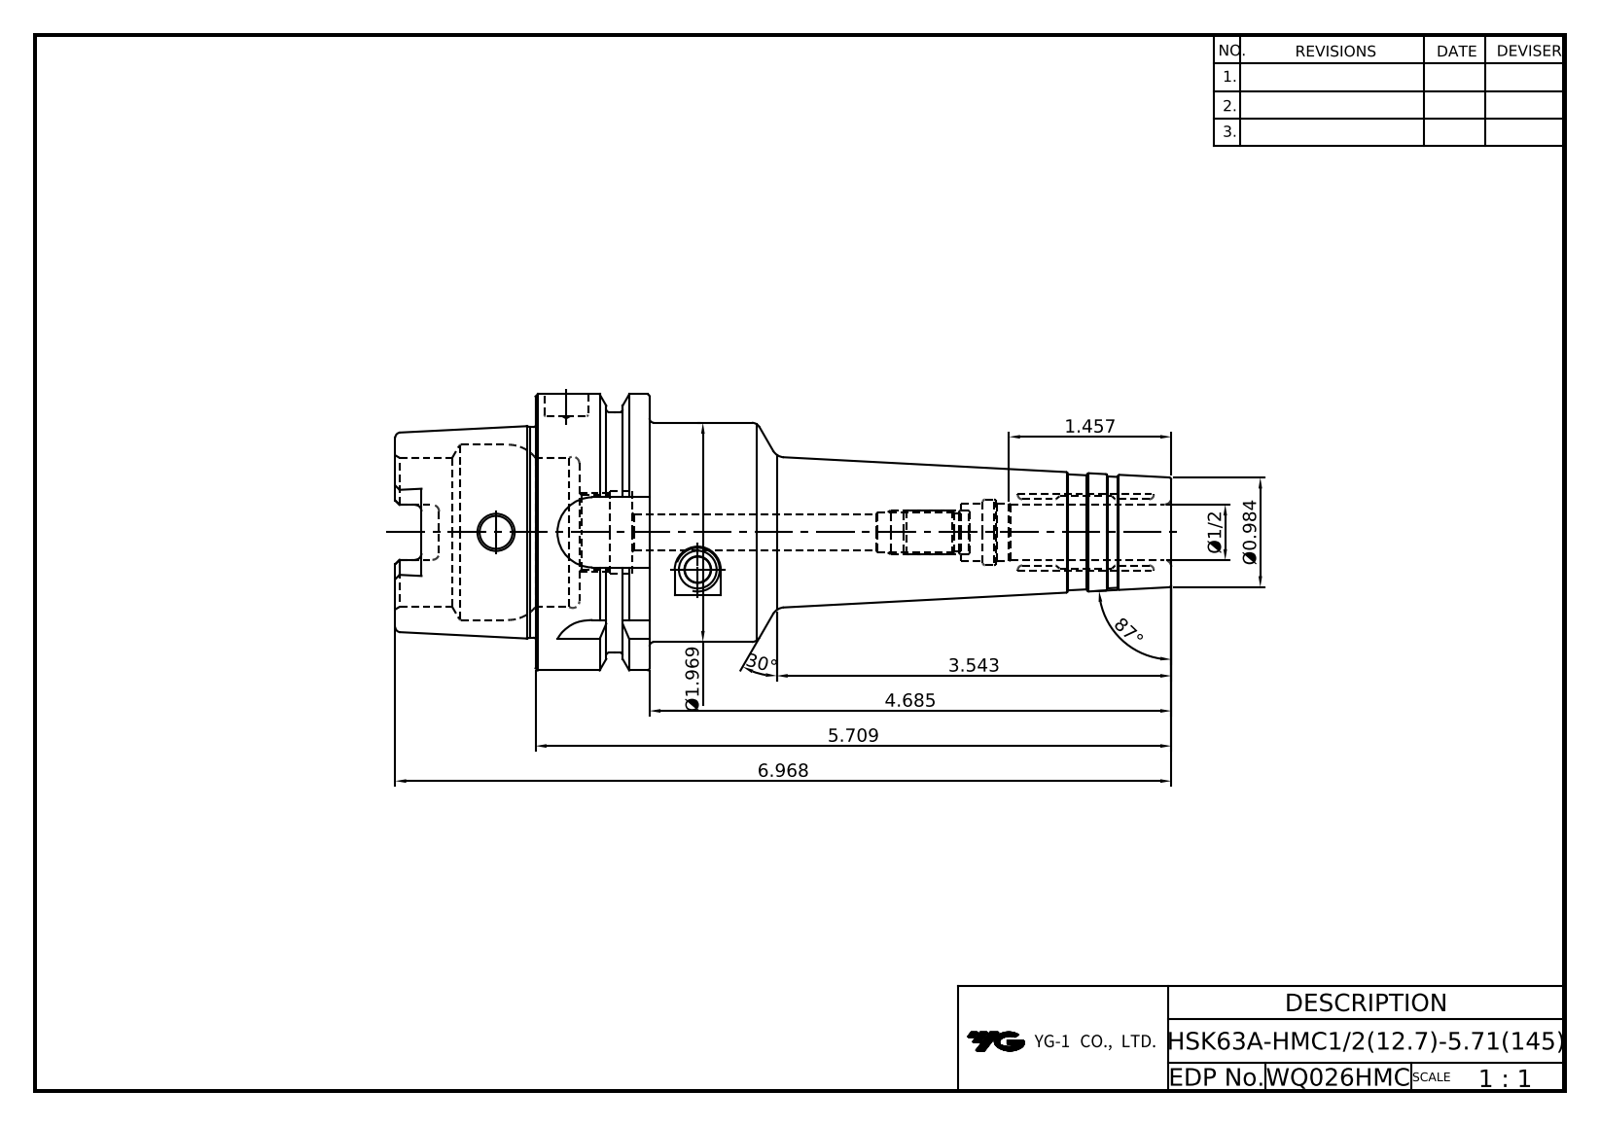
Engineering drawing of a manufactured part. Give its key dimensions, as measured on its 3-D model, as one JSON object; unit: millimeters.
{"part_name": "HSK63A-HMC12_7-145", "step_written_by": "CREO PARAMETRIC BY PTC INC, 2018100 (CONFIG_CONTROL_DESIGN)", "units": "millimeters", "bodies": {"solids": 1, "faces": 177, "planar": 64, "cylindrical": 51, "other": 62}, "overall_size": [177, 63, 63], "volume_mm3": 193319, "surface_area_mm2": 38970, "round_holes": [[10, 2], [7.5, 1], [8, 1], [10.5, 1], [12.7, 1], [17, 1], [18, 1], [19, 1], [34, 1], [40, 1]], "round_bosses_or_shafts": [[63, 1], [55, 1], [50, 1], [48.04, 1]], "partial_cylinders_radius": [[1.5, 6], [2.88, 4], [8, 4]], "face_to_face_distances": [26, 10, 16, 32, 6.12, 9.88, 42, 58, 119, 4], "hole_center_spacings": [46.78]}
